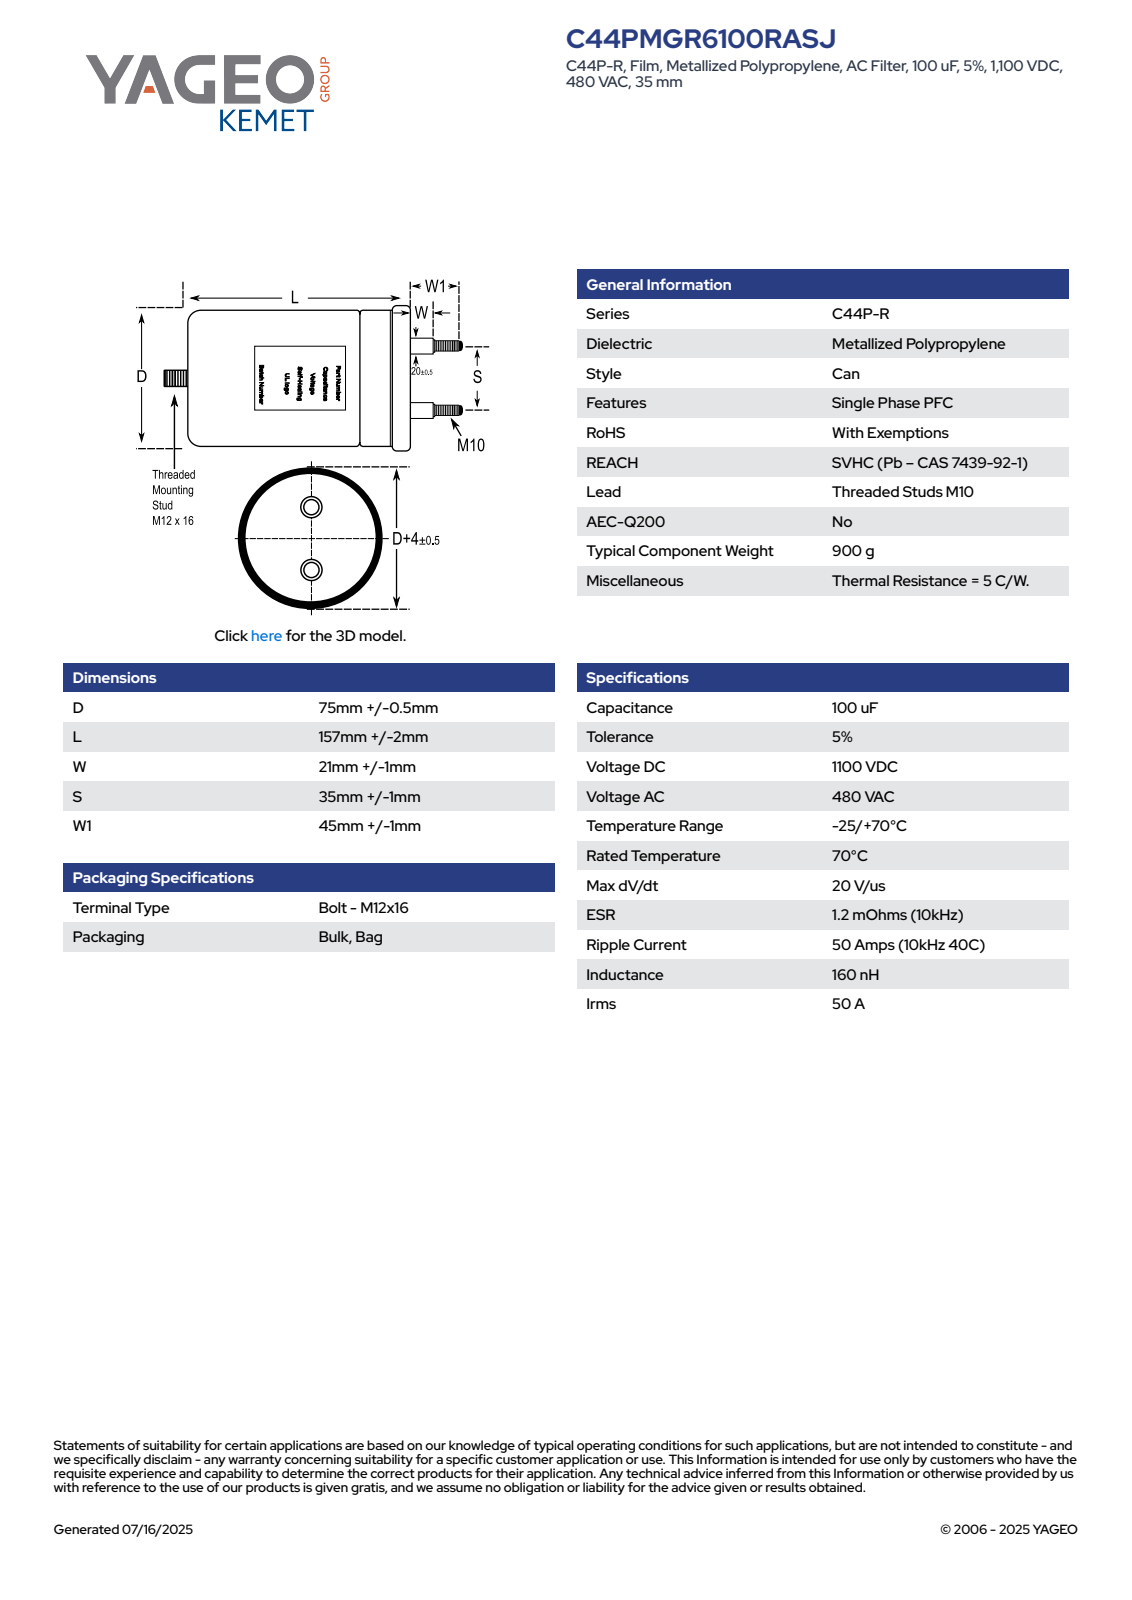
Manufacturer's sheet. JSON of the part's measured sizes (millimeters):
{"part_name": "CFP_C44P_75X157_D75.5L159S35", "step_written_by": "SolidWorks 2014 (AUTOMOTIVE_DESIGN)", "units": "millimeters", "bodies": {"solids": 1, "faces": 105, "planar": 32, "cylindrical": 36, "other": 37}, "overall_size": [221, 80, 80], "volume_mm3": 732972, "surface_area_mm2": 51996, "round_bosses_or_shafts": [[12, 3], [20.5, 2], [10, 2], [80, 1], [75.5, 1]], "partial_cylinders_radius": [[37.76, 1]], "face_to_face_distances": [159, 180, 21, 153.9, 5.1, 26.1, 205, 51.1, 46, 25]}
